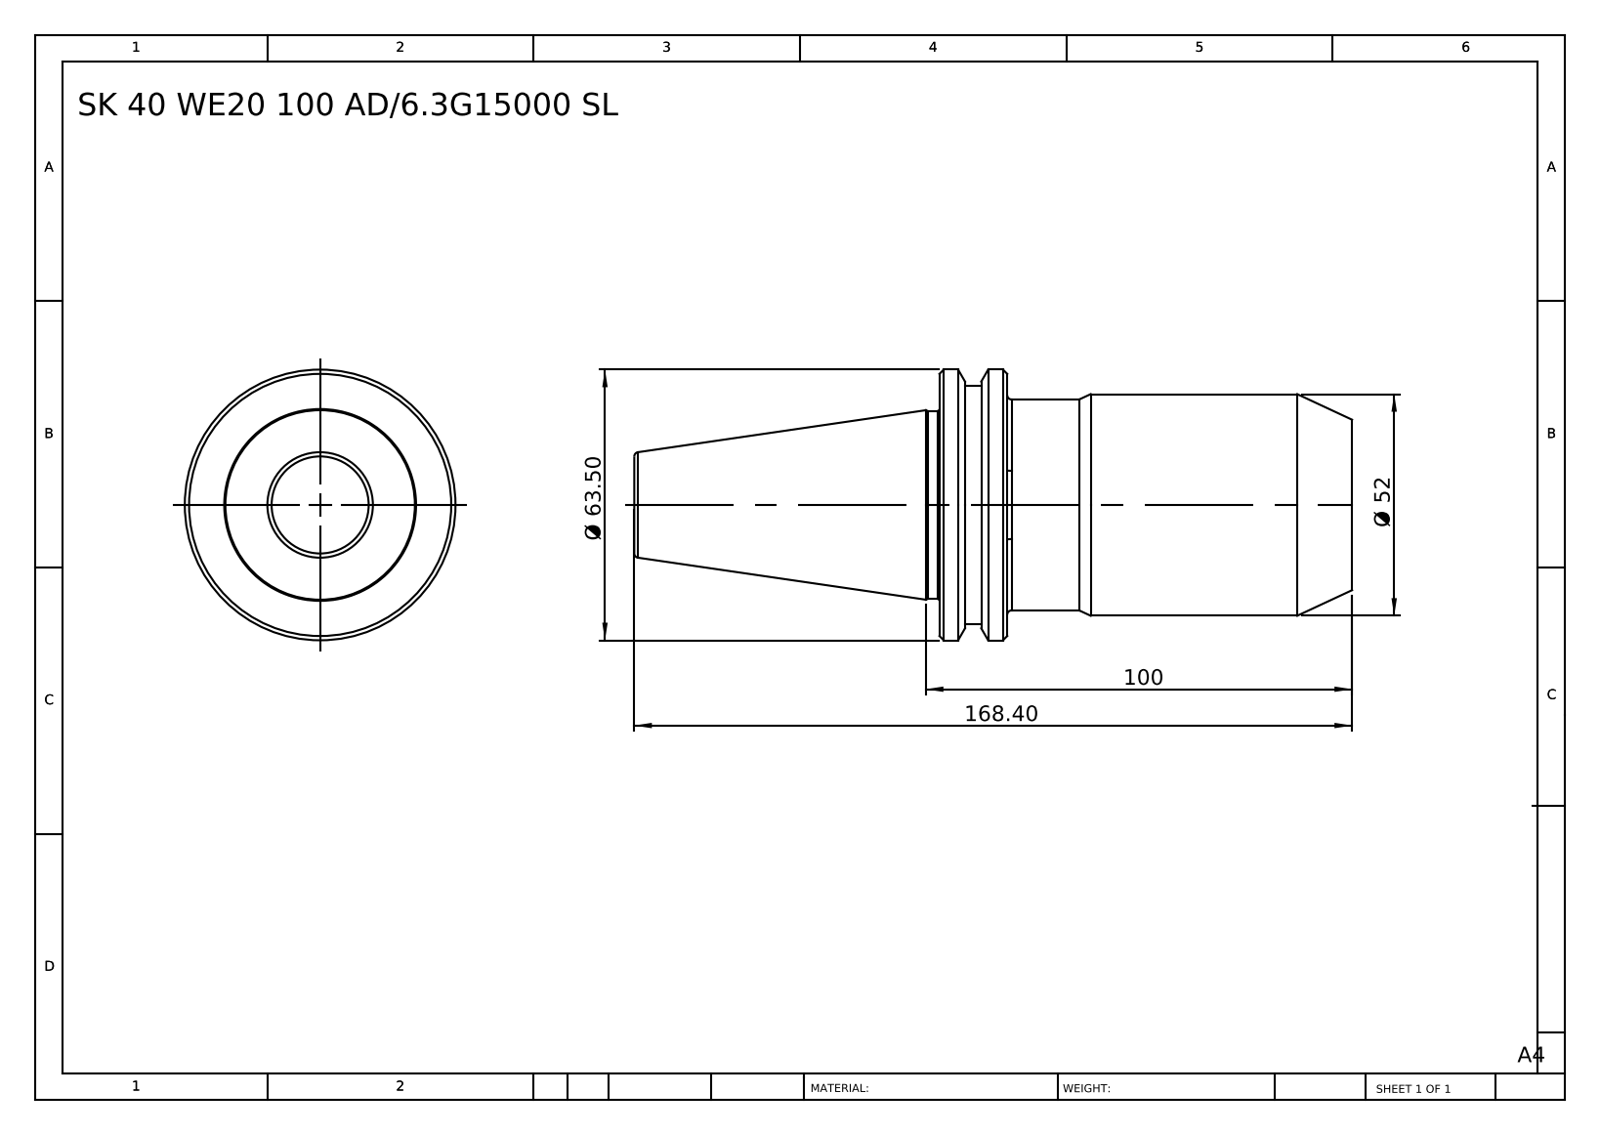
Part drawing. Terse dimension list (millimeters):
name: SK40 WE20 100 AD-6.3G15000 SL
written by: SolidWorks 2014 (CONFIG_CONTROL_DESIGN)
unit: mm
bodies: 1 solid, 40 faces (6 planar, 12 cylindrical, 22 other)
size: 168.4 × 63.5 × 63.5
volume: 279 490 mm³; area: 29 274 mm²
bosses: 1× ⌀63.5, 1× ⌀56, 1× ⌀52, 1× ⌀49.5, 1× ⌀44
face distances: 96.8, 80.9, 15.9, 168.4, 87.5, 71.6, 87, 6.1, 9.8, 81.4
